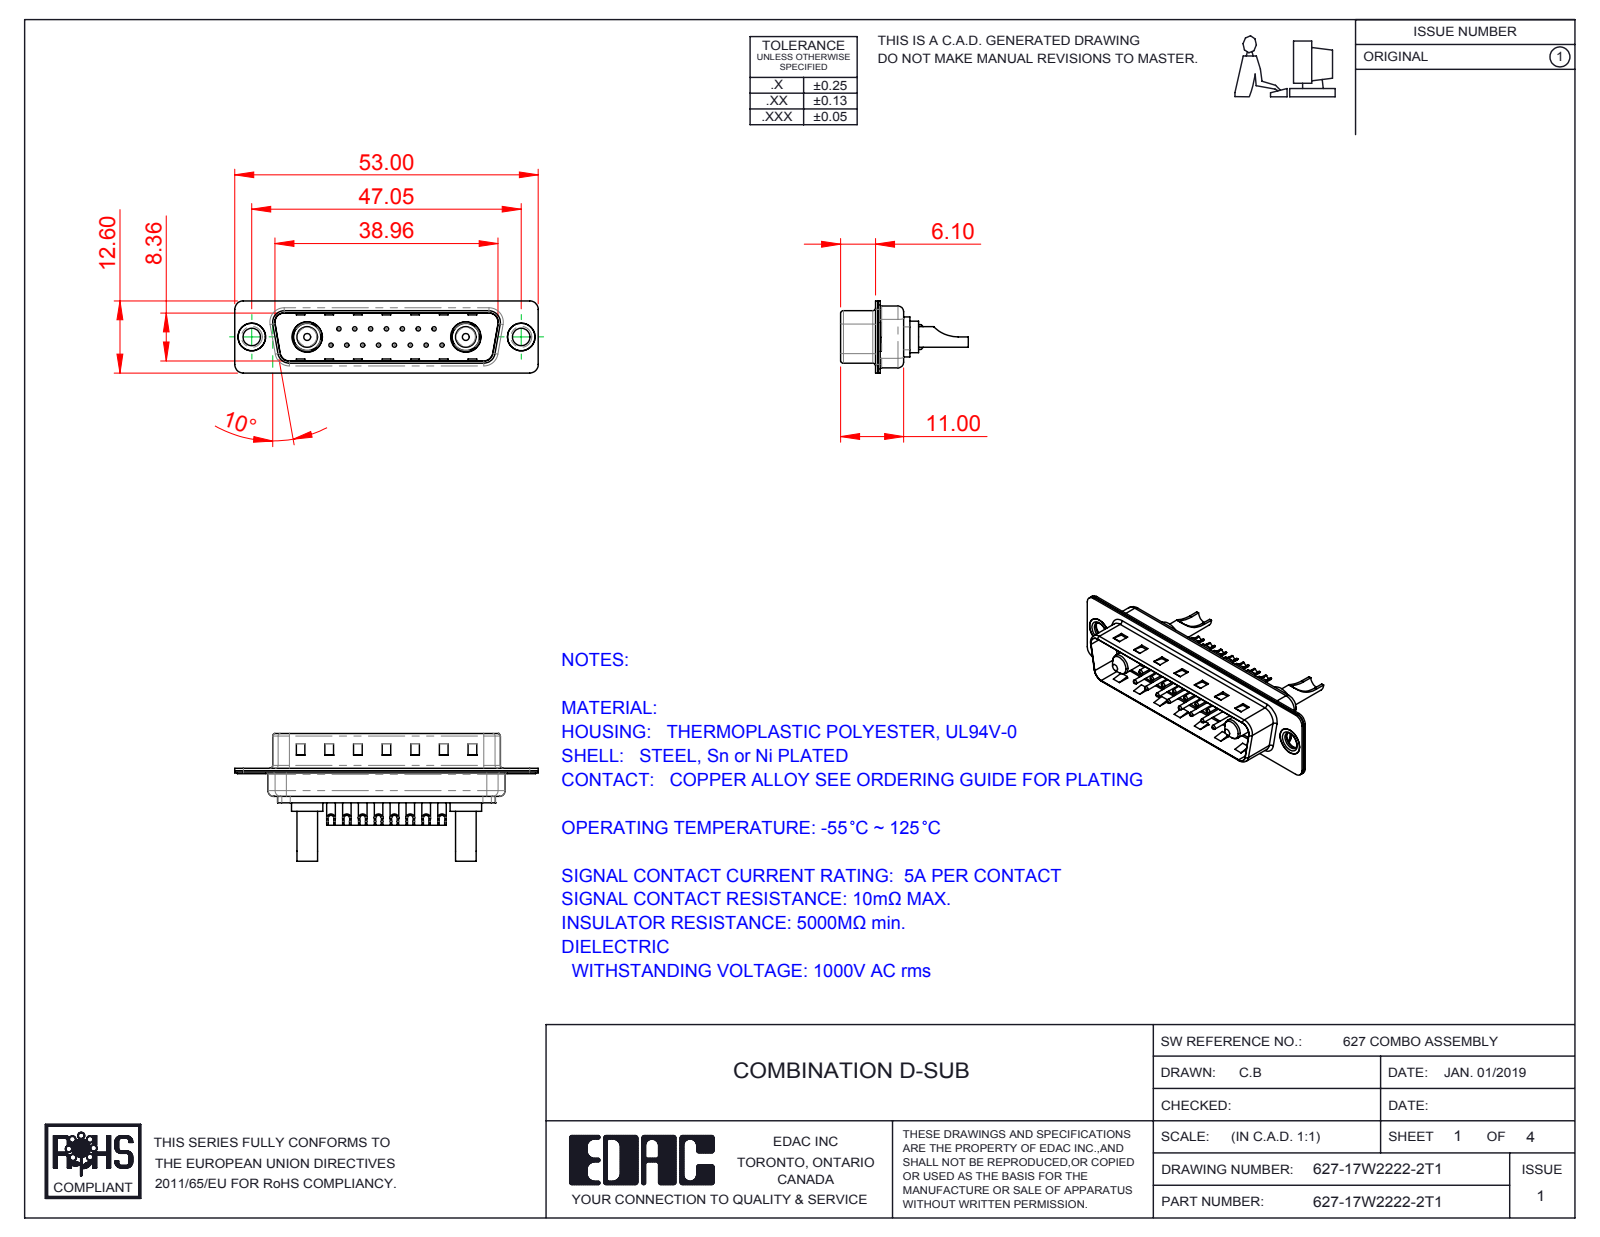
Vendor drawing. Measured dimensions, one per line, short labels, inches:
name: 627-17W2222-2T1; 627Combo Contact Row 2_22; 627Combo Contact Row 1_22; 627Combo Shell Front_25 Contacts (+4 more)
written by: SolidWorks 2016 (CONFIG_CONTROL_DESIGN)
unit: in
bodies: 24 solids, 997 faces (332 planar, 405 cylindrical, 260 other)
size: 2.087 × 0.878 × 0.496
volume: 0.173 in³; area: 10.74 in²
holes: 15× ⌀0.03, 15× ⌀0.039, 15× ⌀0.063, 15× ⌀0.079, 2× ⌀0.106, 2× ⌀0.12, 2× ⌀0.157, 2× ⌀0.189, 2× ⌀0.191, 2× ⌀0.209
bosses: 15× ⌀0.059, 2× ⌀0.217, 2× ⌀0.205, 2× ⌀0.197, 2× ⌀0.193, 2× ⌀0.187, 2× ⌀0.148, 2× ⌀0.142
rounds: 16× R0.059, 12× R0.079, 8× R0.02, 8× R0.063, 6× R0.039, 4× R0.01, 4× R0.024, 4× R0.026
face distances: 0.016, 0.032, 0.377, 0.345, 0.059, 0.22, 0.205, 0.031, 0.048, 0.393
hole spacings: 0.124, 0.109, 0.218, 0.327, 0.198, 0.295, 0.436, 0.198
